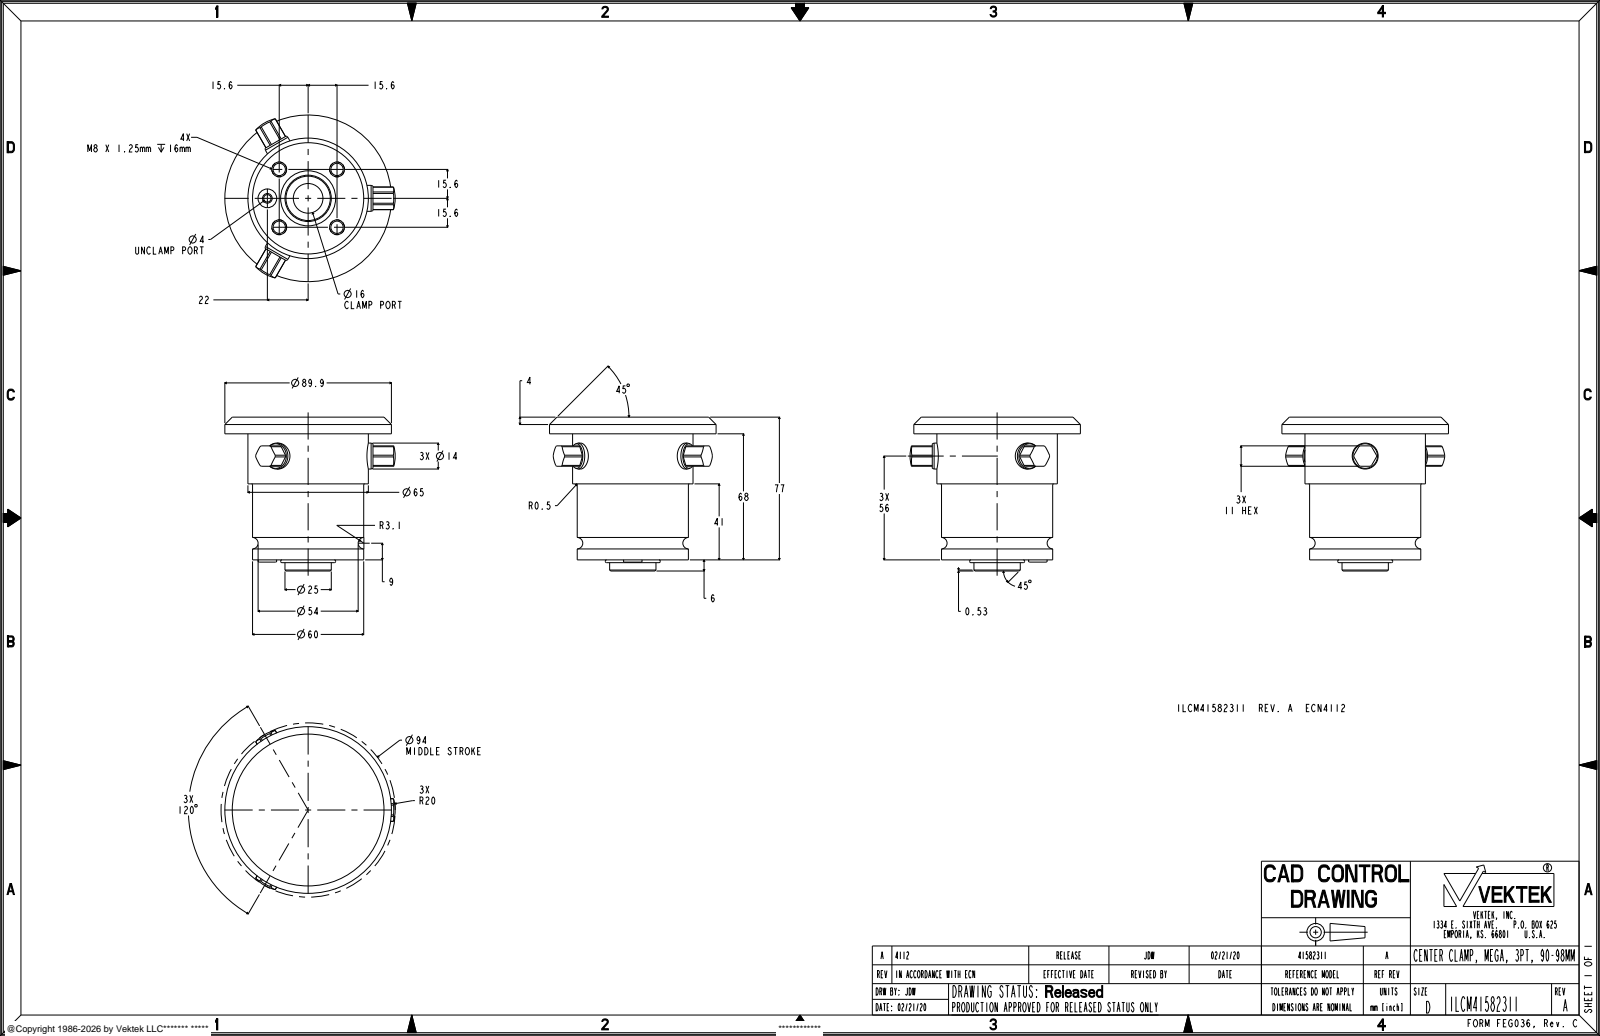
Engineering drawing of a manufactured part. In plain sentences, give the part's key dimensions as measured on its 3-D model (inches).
The part is named "ILCM41582311". Its 3-D file was written by "PRO/ENGINEER BY PARAMETRIC TECHNOLOGY CORPORATION, 2013320 (AUTOMOTIVE_DESIGN)". It is 1 solid with 158 faces: 46 planar, 64 cylindrical and 48 other. Overall it measures 3.62 by 3.539 by 3.268 inches. Its volume is 15.96 cubic inches and its surface area 54.76 square inches. Round holes: 4 of diameter 0.262, 3 of diameter 0.551, 1 of diameter 0.157, 1 of diameter 0.63. Round bosses or shafts: 4 of diameter 0.315, 1 of diameter 3.539, 1 of diameter 2.559, 1 of diameter 2.362, 1 of diameter 1.169, 1 of diameter 0.984. Partial cylindrical surfaces (rounded edges, fillets, slot ends): 3 of radius 0.24. The main face-to-face distances are 0.354, 2.677, 3.031, 0.433, 0.098, 0.118, 1.614, 1.063, 1.417, 0.236. The hole center spacings are 0.869, 1.228, 0.664, 1.603, 1.737, 0.866.
